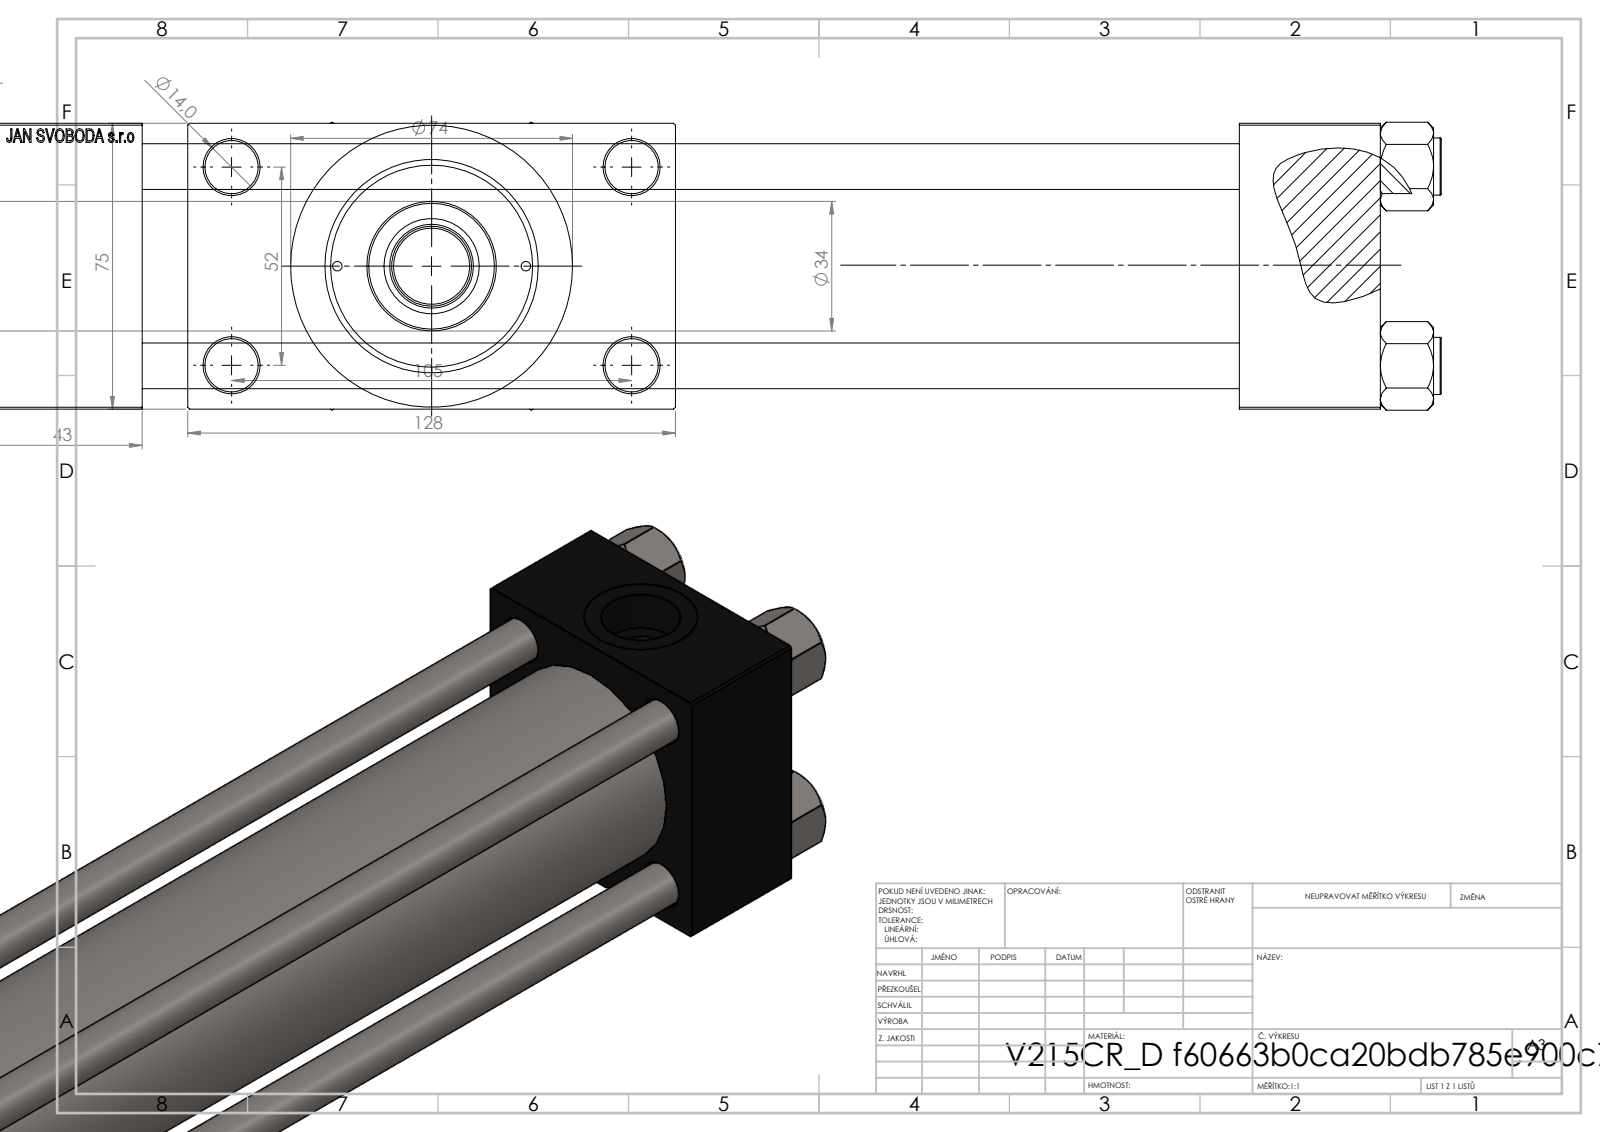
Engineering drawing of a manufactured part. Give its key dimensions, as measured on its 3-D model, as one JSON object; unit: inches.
{"part_name": "V215_VC_A; V215CR_ROD_END_F; NUT_M5_D; V215CR_VCP_D (+2 more)", "step_written_by": "SolidWorks 2019 (CONFIG_CONTROL_DESIGN)", "units": "inches", "bodies": {"solids": 12, "faces": 1123, "planar": 502, "cylindrical": 97, "other": 524}, "overall_size": [17.835, 5.039, 2.974], "volume_in3": 68.29, "surface_area_in2": 456, "round_holes": [[0.472, 4], [0.551, 4], [0.098, 2], [0.276, 2], [0.825, 2], [1.181, 2], [0.413, 1], [0.866, 1], [0.984, 1], [1.614, 1], [1.969, 1], [2.087, 1]], "round_bosses_or_shafts": [[0.591, 4], [2.913, 1], [2.205, 1], [1.339, 1], [0.827, 1], [0.512, 1]], "face_to_face_distances": [2.953, 11.339, 1.457, 12.795, 1.043, 3.996, 14.488, 13.031, 1.693, 0.63], "hole_center_spacings": [1.031, 1.037, 1.456, 1.497, 2.059, 2.253, 2.3, 2.307]}
